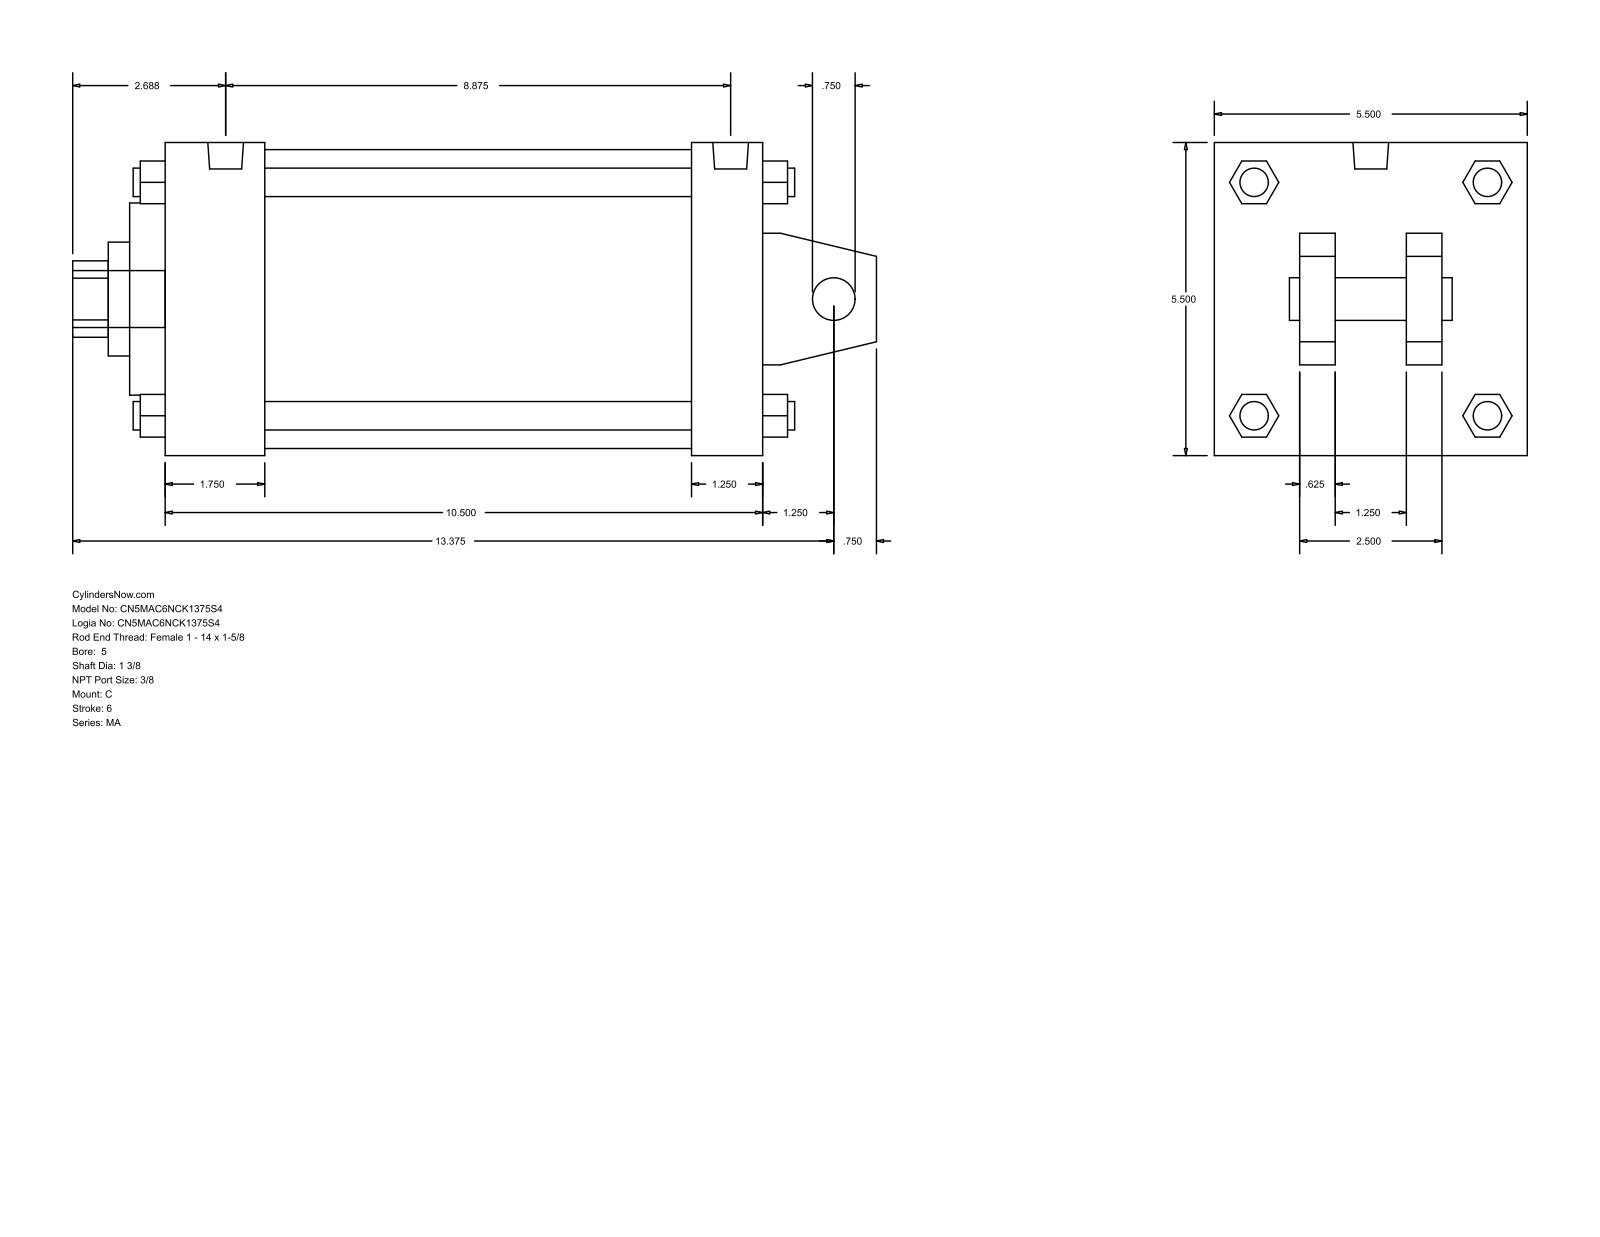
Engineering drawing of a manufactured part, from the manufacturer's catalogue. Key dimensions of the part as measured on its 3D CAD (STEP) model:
Part name (STEP PRODUCT): MA_C__0500_1.375
STEP written by: GSSL Pune (CONFIG_CONTROL_DESIGN)
Units: millimetres
Bodies: 0 solids, 141 faces (109 planar, 32 cylindrical, 0 other)
Overall size (bounding box): 358.77 × 139.7 × 139.7
Round holes (diameter × count): ⌀19.05 ×1, ⌀34.92 ×1, ⌀50.8 ×1, ⌀85.72 ×1, ⌀133.35 ×1
Round bosses / shafts (diameter × count): ⌀12.7 ×4, ⌀11.11 ×4, ⌀15.93 ×2, ⌀25.4 ×1
Partial cylindrical surfaces — rounded edges, fillets, slot ends (radius × count): R17.06 ×1
Main face-to-face distances: 139.7, 266.71, 15.87, 234.96, 31.75, 44.45, 190.51, 222.26, 38.1, 101.6
